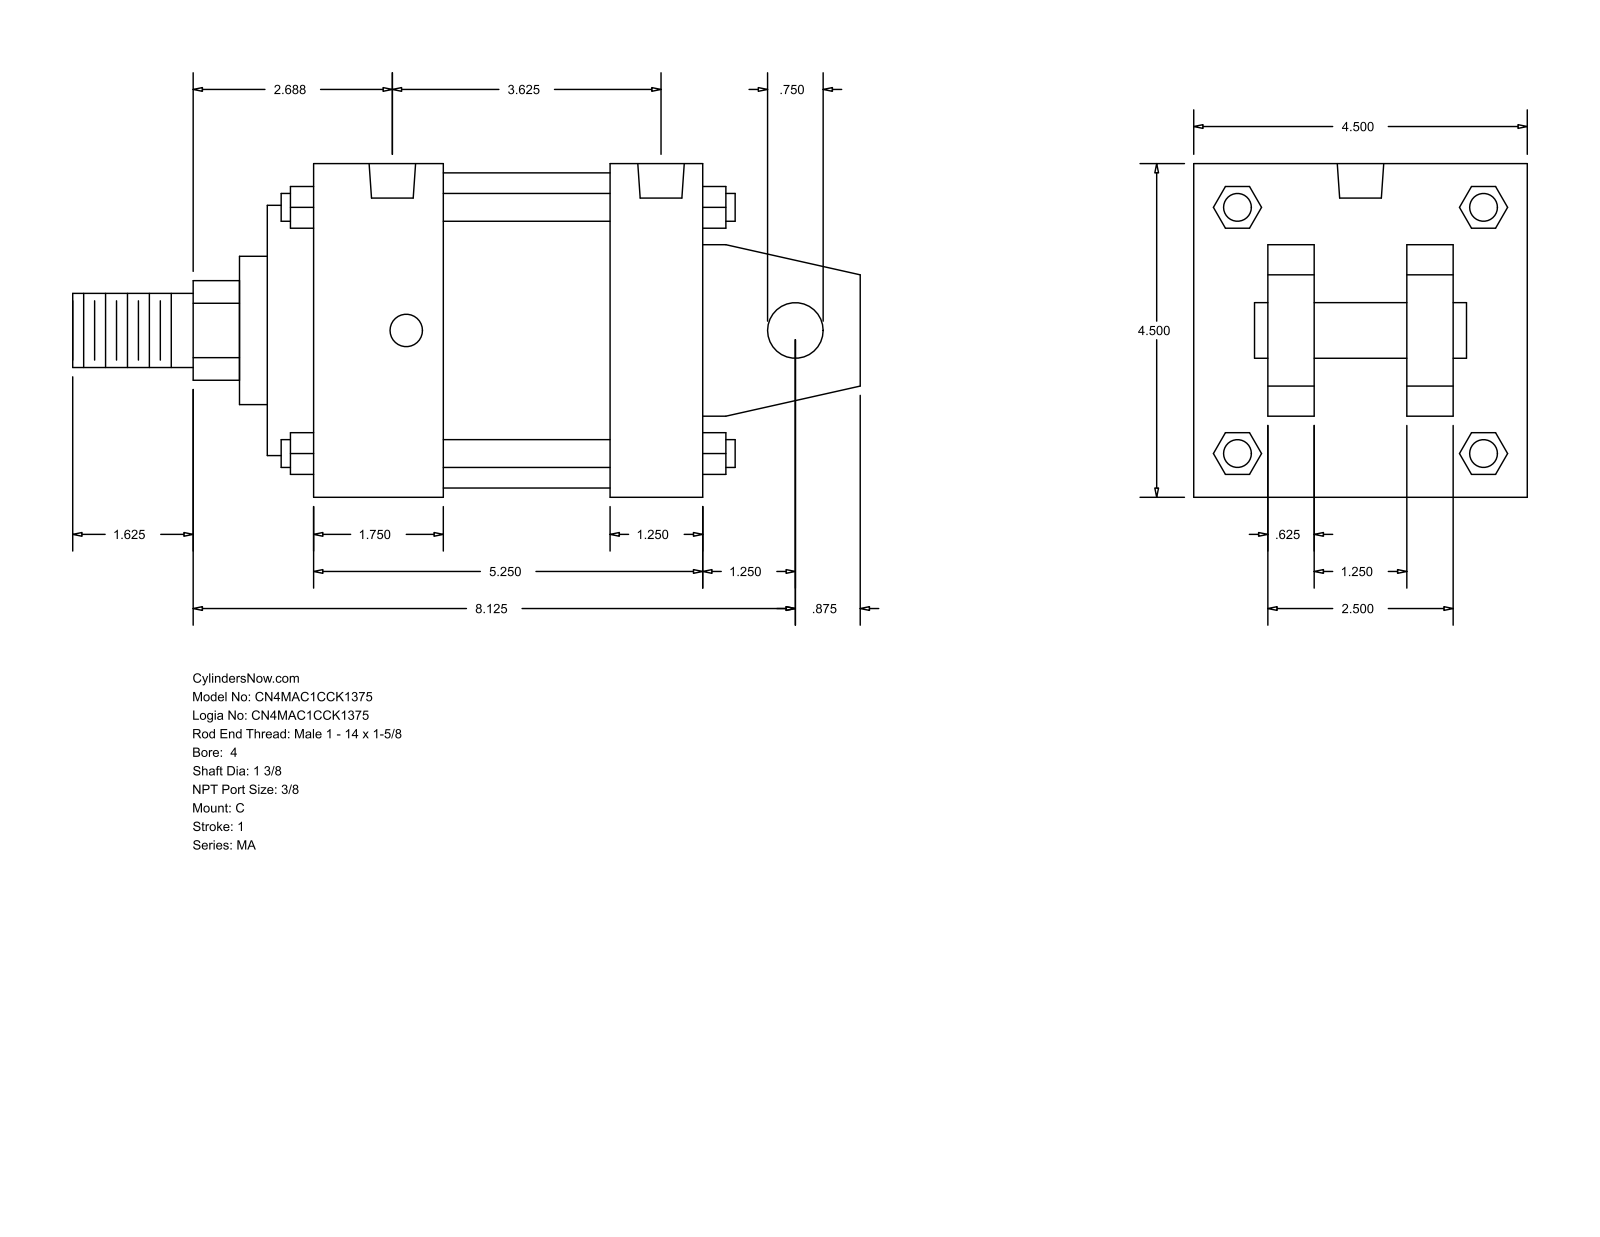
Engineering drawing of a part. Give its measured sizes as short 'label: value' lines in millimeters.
name: MA_C__0400_1.375
written by: GSSL Pune (CONFIG_CONTROL_DESIGN)
unit: mm
bodies: 0 solids, 141 faces (109 planar, 32 cylindrical, 0 other)
size: 269.88 × 114.3 × 114.3
holes: 4× ⌀11.11, 2× ⌀15.93
bosses: 4× ⌀9.53, 1× ⌀107.95, 1× ⌀85.72, 1× ⌀50.8, 1× ⌀34.92, 1× ⌀25.4, 1× ⌀19.05
rounds: 1× R17.06
face distances: 114.3, 15.87, 88.9, 133.35, 73.03, 41.27, 25.4, 47.63, 149.22, 117.48
hole spacings: 4.77, 82.54, 87.31, 92.08
